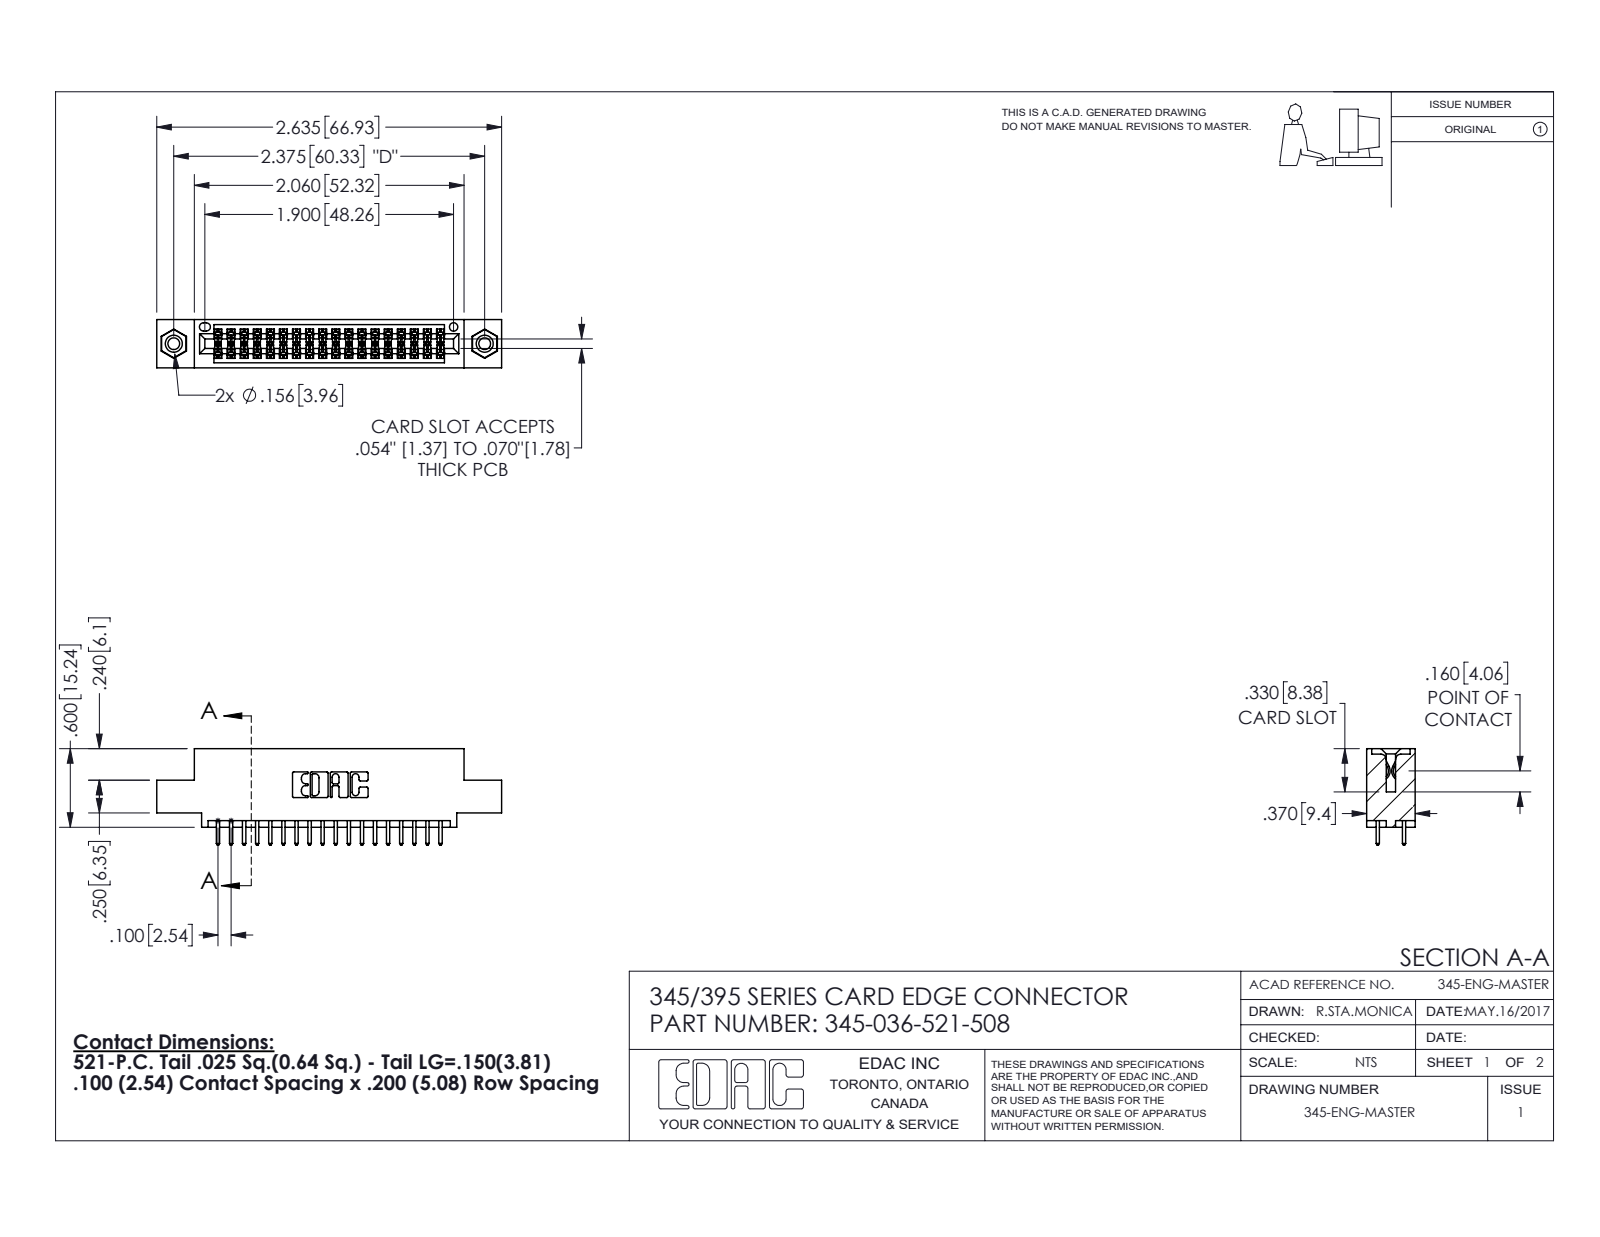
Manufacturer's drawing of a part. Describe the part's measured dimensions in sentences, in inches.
The part is named "345-292-001_345-293-121; 345 Part_0.110 Offset - 0.156 Dia-TI; 345-036-521-508; 345-250-001_345-250-003-102". Its 3-D file was written by "SolidWorks 2016 (CONFIG_CONTROL_DESIGN)". It is 39 solids with 1990 faces: 1304 planar, 670 cylindrical and 16 other. Overall it measures 2.635 by 0.737 by 0.37 inches. Its volume is 0.377 cubic inches and its surface area 13.47 square inches. Round holes: 2 of diameter 0.089, 2 of diameter 0.125, 2 of diameter 0.156, 1 of diameter 0.064. Round bosses or shafts: 2 of diameter 0.155. Partial cylindrical surfaces (rounded edges, fillets, slot ends): 54 of radius 0.006, 36 of radius 0.01, 22 of radius 0.01, 6 of radius 0.007, 6 of radius 0.031, 3 of radius 0.026, 2 of radius 0.014, 2 of radius 0.019. The main face-to-face distances are 0.072, 0.298, 0.2, 0.37, 0.098, 0.272, 0.025, 0.225, 0.175, 0.1. The hole center spacings are 0.27, 2.141, 2.375.
